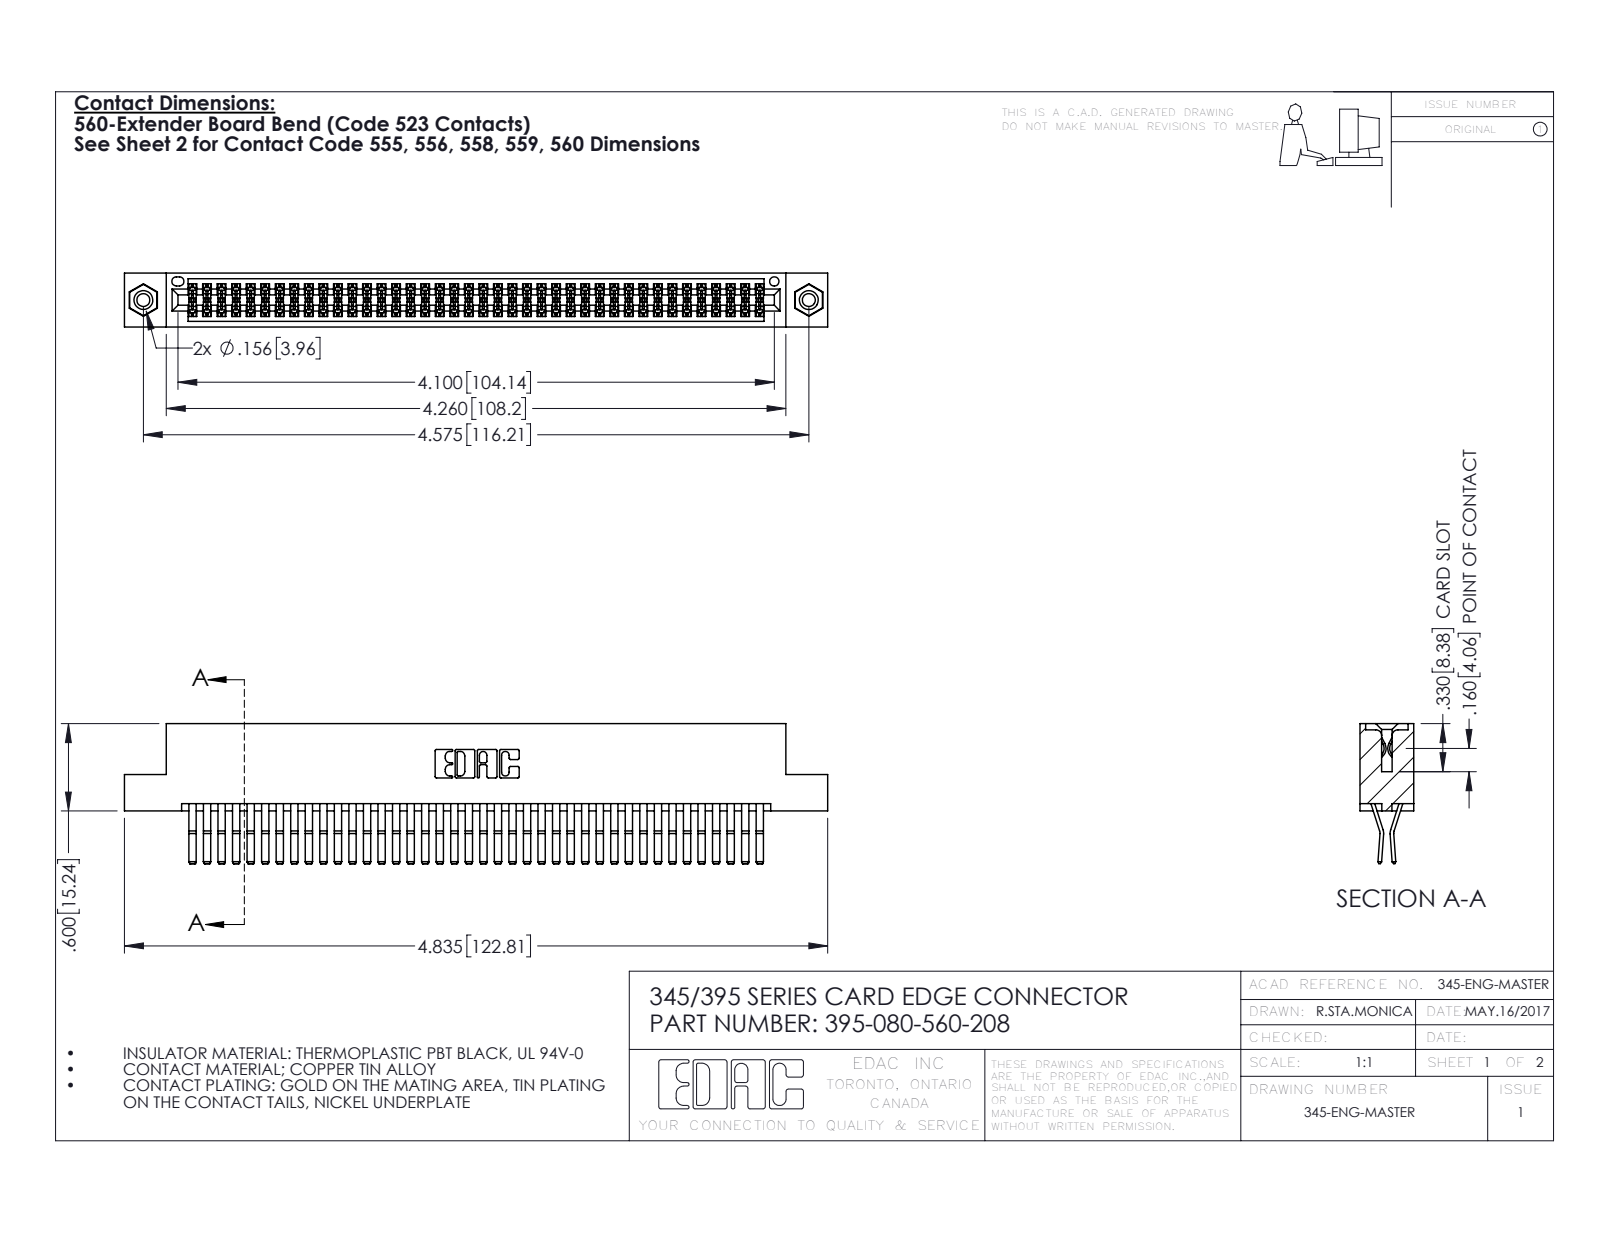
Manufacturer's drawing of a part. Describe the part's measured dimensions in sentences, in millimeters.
The part is named "345-250-001_345-250-003-102; 345-292-001_560 Tail; 345 Part_Flush Mounting Lugs - 0.156 Dia-TI; 395-080-560-208". Its 3-D file was written by "SolidWorks 2016 (CONFIG_CONTROL_DESIGN)". It is 83 solids with 4346 faces: 2752 planar, 1578 cylindrical and 16 other. Overall it measures 122.8 by 24.4 by 9.4 millimeters. Its volume is 12 400 cubic millimeters and its surface area 19 700 square millimeters. Round holes: 2 of diameter 2.3, 2 of diameter 3.2, 2 of diameter 4, 1 of diameter 1.6. Round bosses or shafts: 2 of diameter 3.9. Partial cylindrical surfaces (rounded edges, fillets, slot ends): 120 of radius 0.2, 22 of radius 0.3, 6 of radius 0.2, 6 of radius 0.8, 3 of radius 0.7, 2 of radius 0.3, 2 of radius 0.4, 2 of radius 0.5. The main face-to-face distances are 0.6, 1.8, 7.6, 5.1, 9.4, 2.5, 6.9, 5.7, 4.4, 3.8. The hole center spacings are 6.9, 110.2, 116.2.
